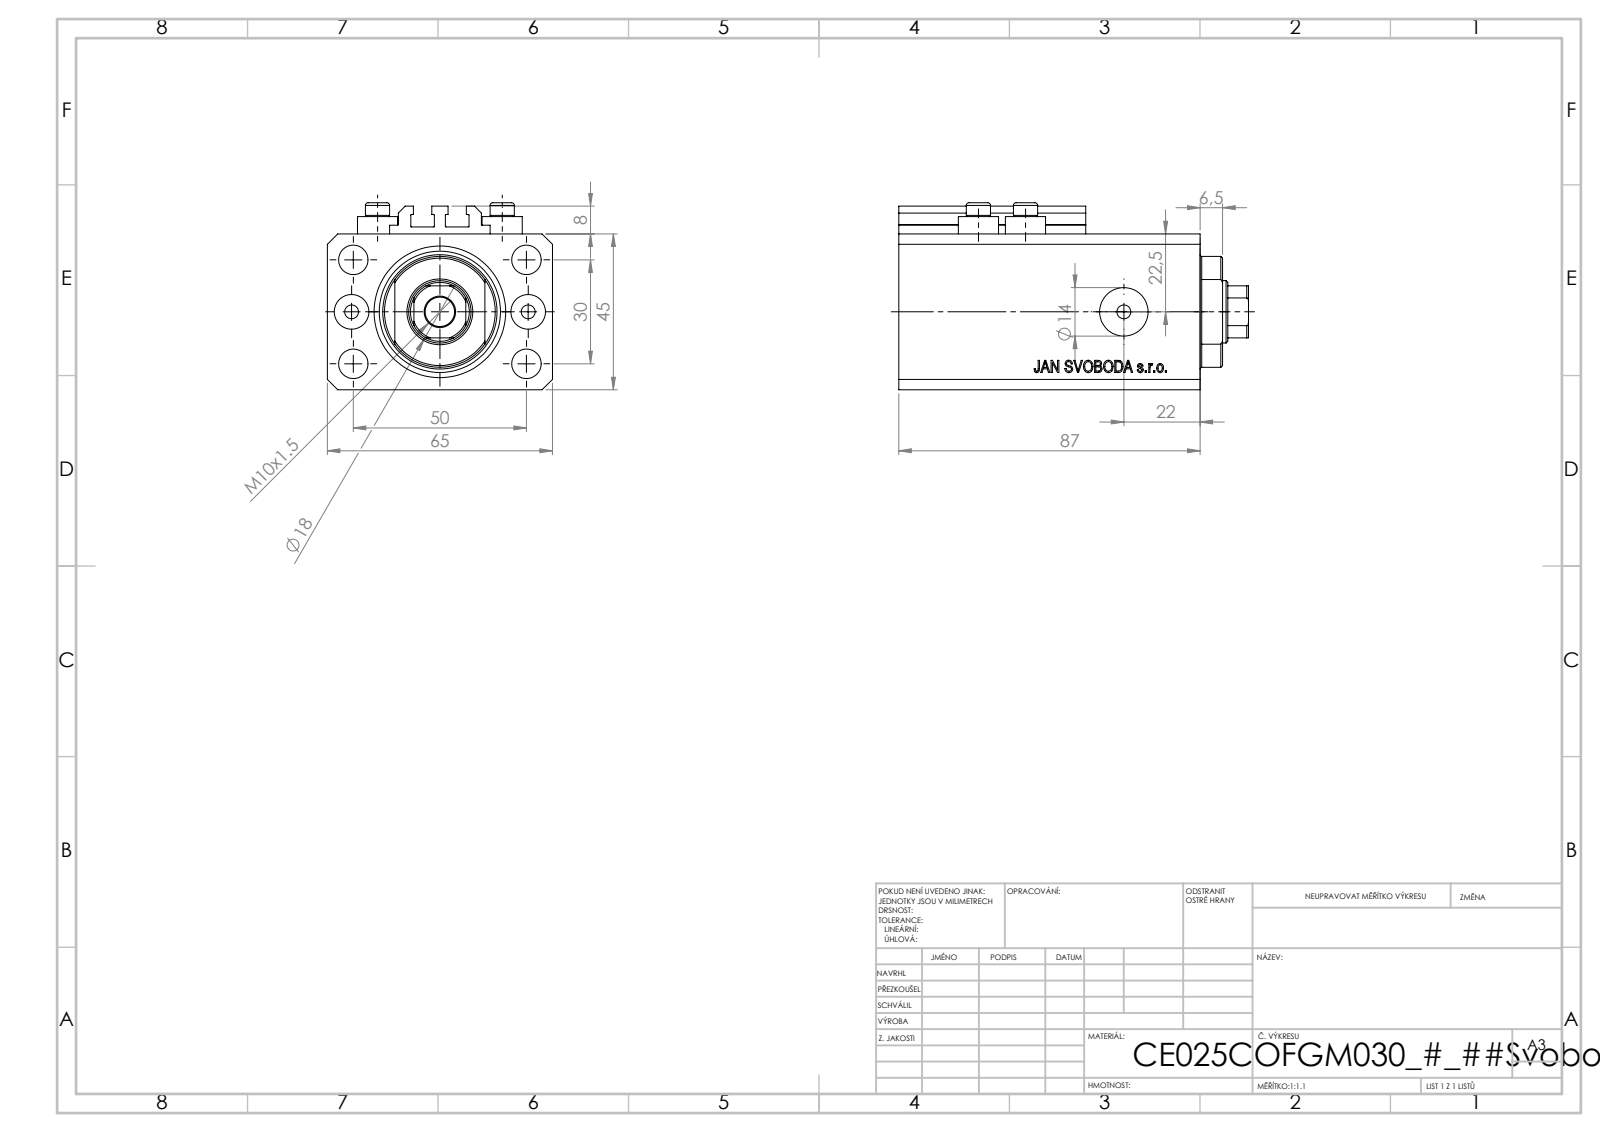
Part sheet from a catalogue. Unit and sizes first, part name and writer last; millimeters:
Units: millimetres
Overall size (bounding box): 101 × 65 × 54
Round holes (diameter × count): ⌀4 ×8, ⌀8.5 ×5, ⌀10 ×2, ⌀14 ×2, ⌀18 ×1, ⌀25 ×1, ⌀38 ×1
Round bosses / shafts (diameter × count): ⌀11.6 ×4, ⌀7 ×4
Partial cylindrical surfaces — rounded edges, fillets, slot ends (radius × count): R0.2 ×10, R8.5 ×1, R16 ×1
Main face-to-face distances: 45, 65, 14, 73, 87, 47, 6.9, 66.1, 80.1, 3
Hole centre spacings: 15.01, 29.15, 52.68, 13.6, 25.5, 30, 36, 38.48
Volume: 237 637 mm³ · Surface area: 62 822 mm²
Bodies: 8 solids, 1034 faces (504 planar, 86 cylindrical, 444 other)
Part name (STEP PRODUCT): V250CE_VC_C; V250CE_C_Body; ALLEN BOLT V250CE; V250CE_C_VCP
STEP written by: SolidWorks 2019 (CONFIG_CONTROL_DESIGN)
